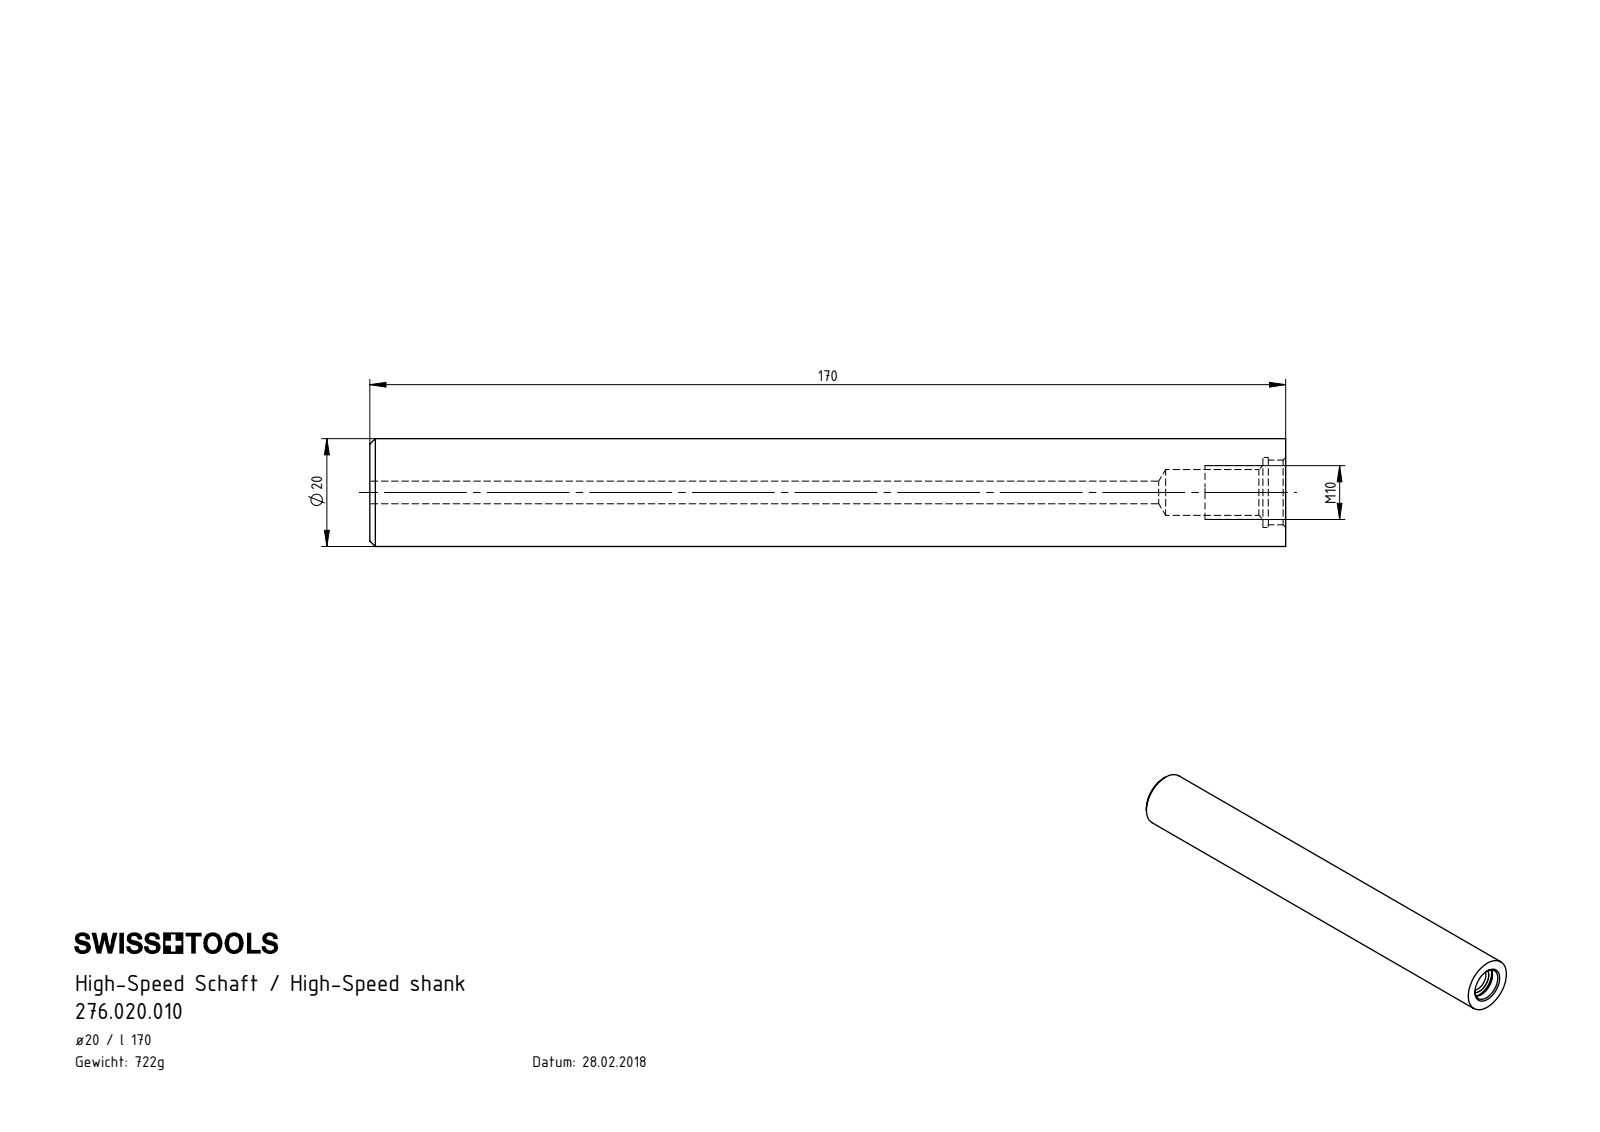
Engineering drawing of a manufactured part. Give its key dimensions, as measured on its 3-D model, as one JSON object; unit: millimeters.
{"part_name": "276.020.010", "step_written_by": "SolidWorks 2017 (CONFIG_CONTROL_DESIGN)", "units": "millimeters", "bodies": {"solids": 1, "faces": 22, "planar": 4, "cylindrical": 10, "other": 8}, "overall_size": [170, 20, 20], "volume_mm3": 49768, "surface_area_mm2": 13846, "round_holes": [[4.2, 1], [8.5, 1], [12, 1], [13, 1]], "round_bosses_or_shafts": [[20, 1]], "face_to_face_distances": [170, 165.75, 4.25, 166.75, 1, 3.25]}
